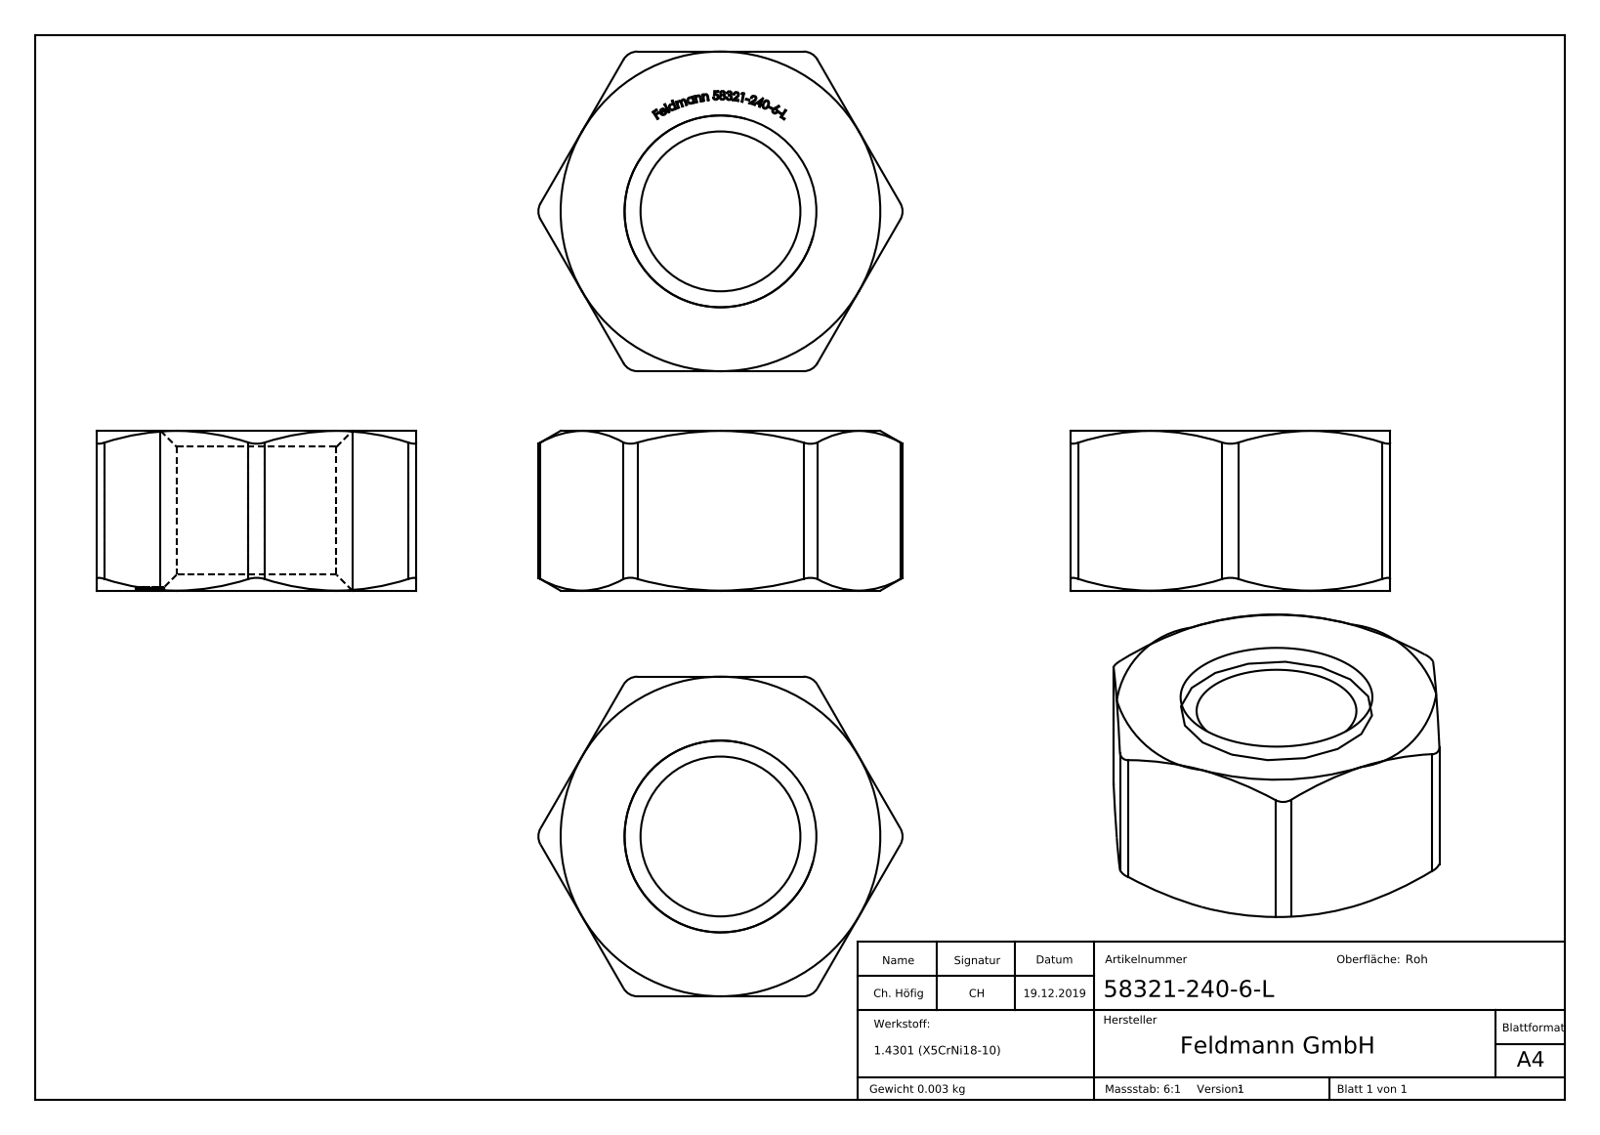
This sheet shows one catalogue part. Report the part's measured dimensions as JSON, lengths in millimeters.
{"part_name": "58321-240-6-L", "step_written_by": "SolidWorks 2015 (CONFIG_CONTROL_DESIGN)", "units": "millimeters", "bodies": {"solids": 1, "faces": 29, "planar": 8, "cylindrical": 7, "other": 14}, "overall_size": [22, 11.39, 10], "volume_mm3": 328, "surface_area_mm2": 368, "round_holes": [[5, 1]], "partial_cylinders_radius": [[0.5, 6]], "face_to_face_distances": [10, 5]}
